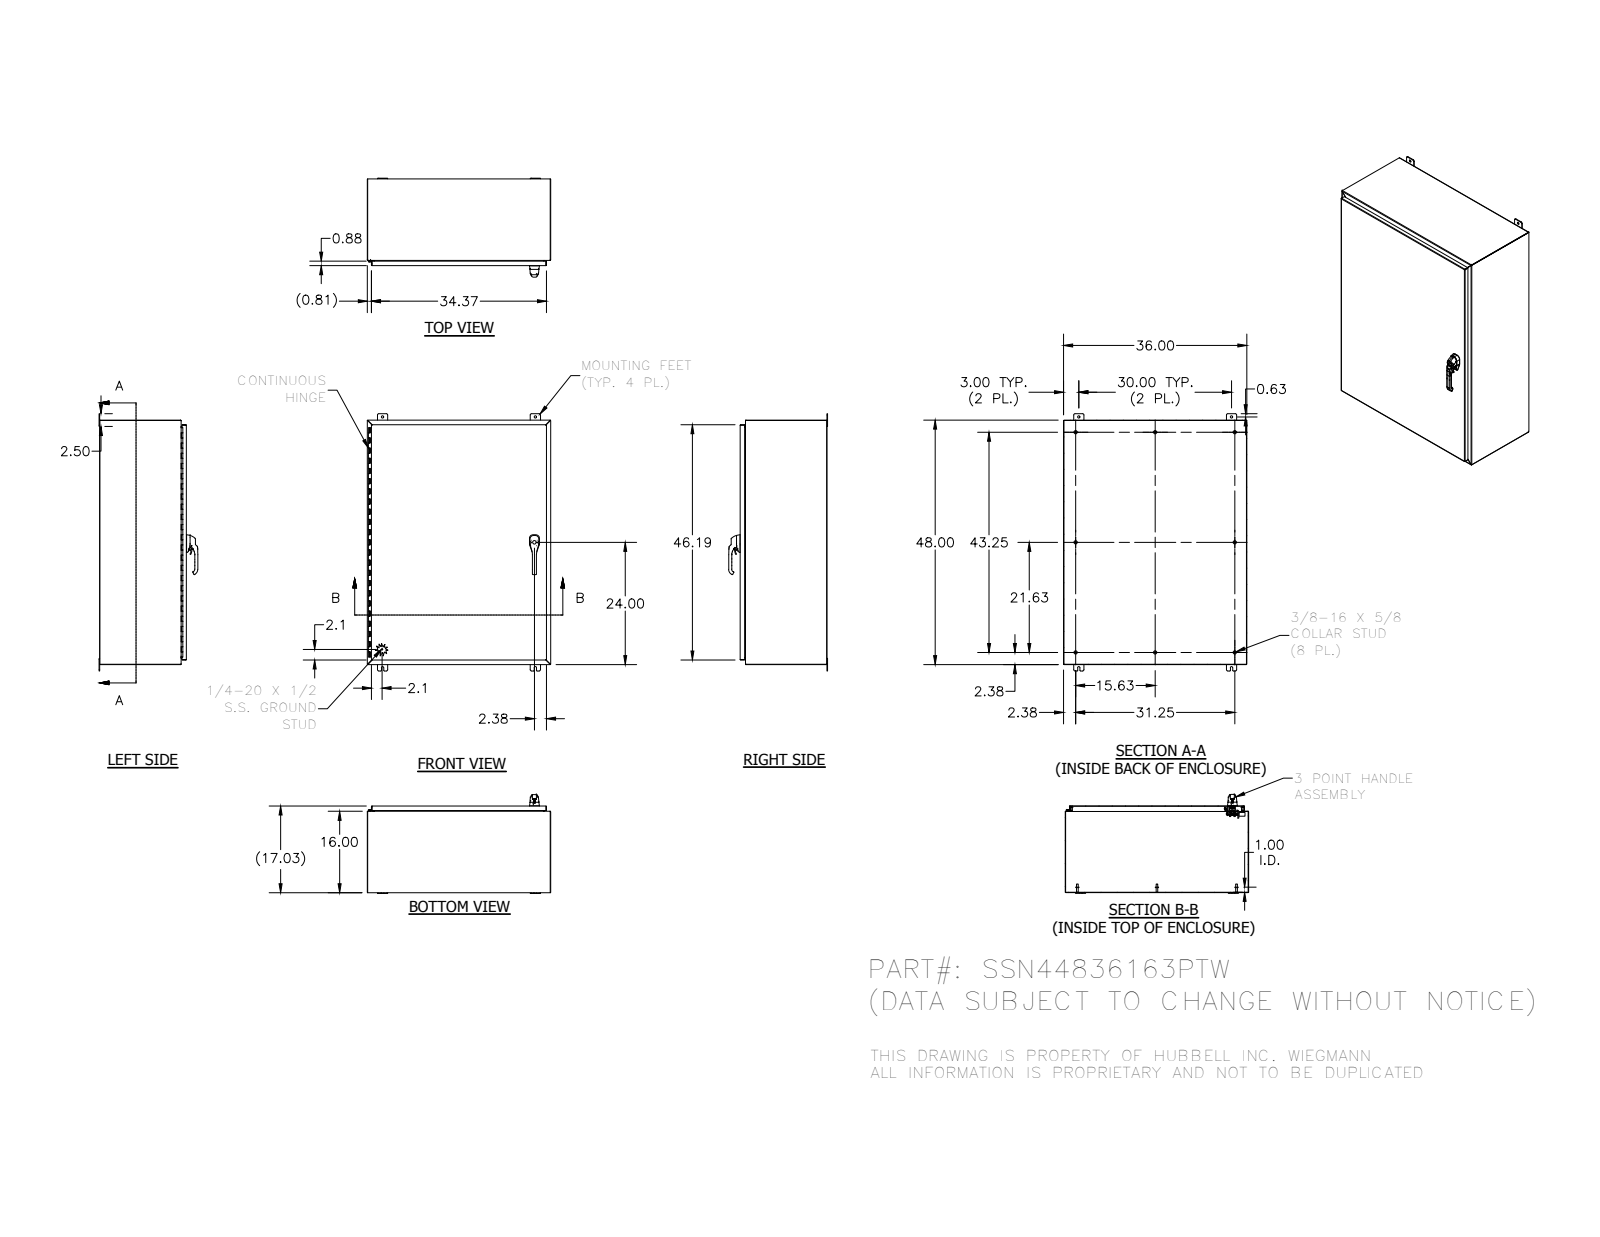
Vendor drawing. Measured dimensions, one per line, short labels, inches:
name: SSN448363PTWLID; 7379-M6-8X25_AF0; DIN985_M10; 32874-48 (+8 more)
written by: SolidWorks 2014 (AUTOMOTIVE_DESIGN)
unit: in
bodies: 62 solids, 3345 faces (1192 planar, 1368 cylindrical, 785 other)
size: 50.5 × 36 × 19.408
volume: 520.9 in³; area: 13 783 in²
holes: 8× ⌀0.262, 4× ⌀0.187, 4× ⌀0.438, 3× ⌀0.213, 3× ⌀0.281, 2× ⌀0.241, 2× ⌀0.25, 2× ⌀0.252, 2× ⌀0.315, 2× ⌀0.4, 2× ⌀0.402, 2× ⌀0.413
bosses: 8× ⌀0.625, 8× ⌀0.33, 3× ⌀0.236, 2× ⌀1, 2× ⌀0.563, 2× ⌀0.533, 2× ⌀0.531, 2× ⌀0.5
rounds: 172× R0.02, 113× R0.012, 26× R0.125, 22× R0.031, 21× R0.019, 20× R0.25, 18× R0.105, 15× R0.05
face distances: 0.074, 16.959, 16.885, 17.033, 35.926, 47.926, 35.852, 36, 47.852, 48
hole spacings: 0.38, 0.492, 0.76, 0.886, 38.428, 0.234, 0.258, 0.38
